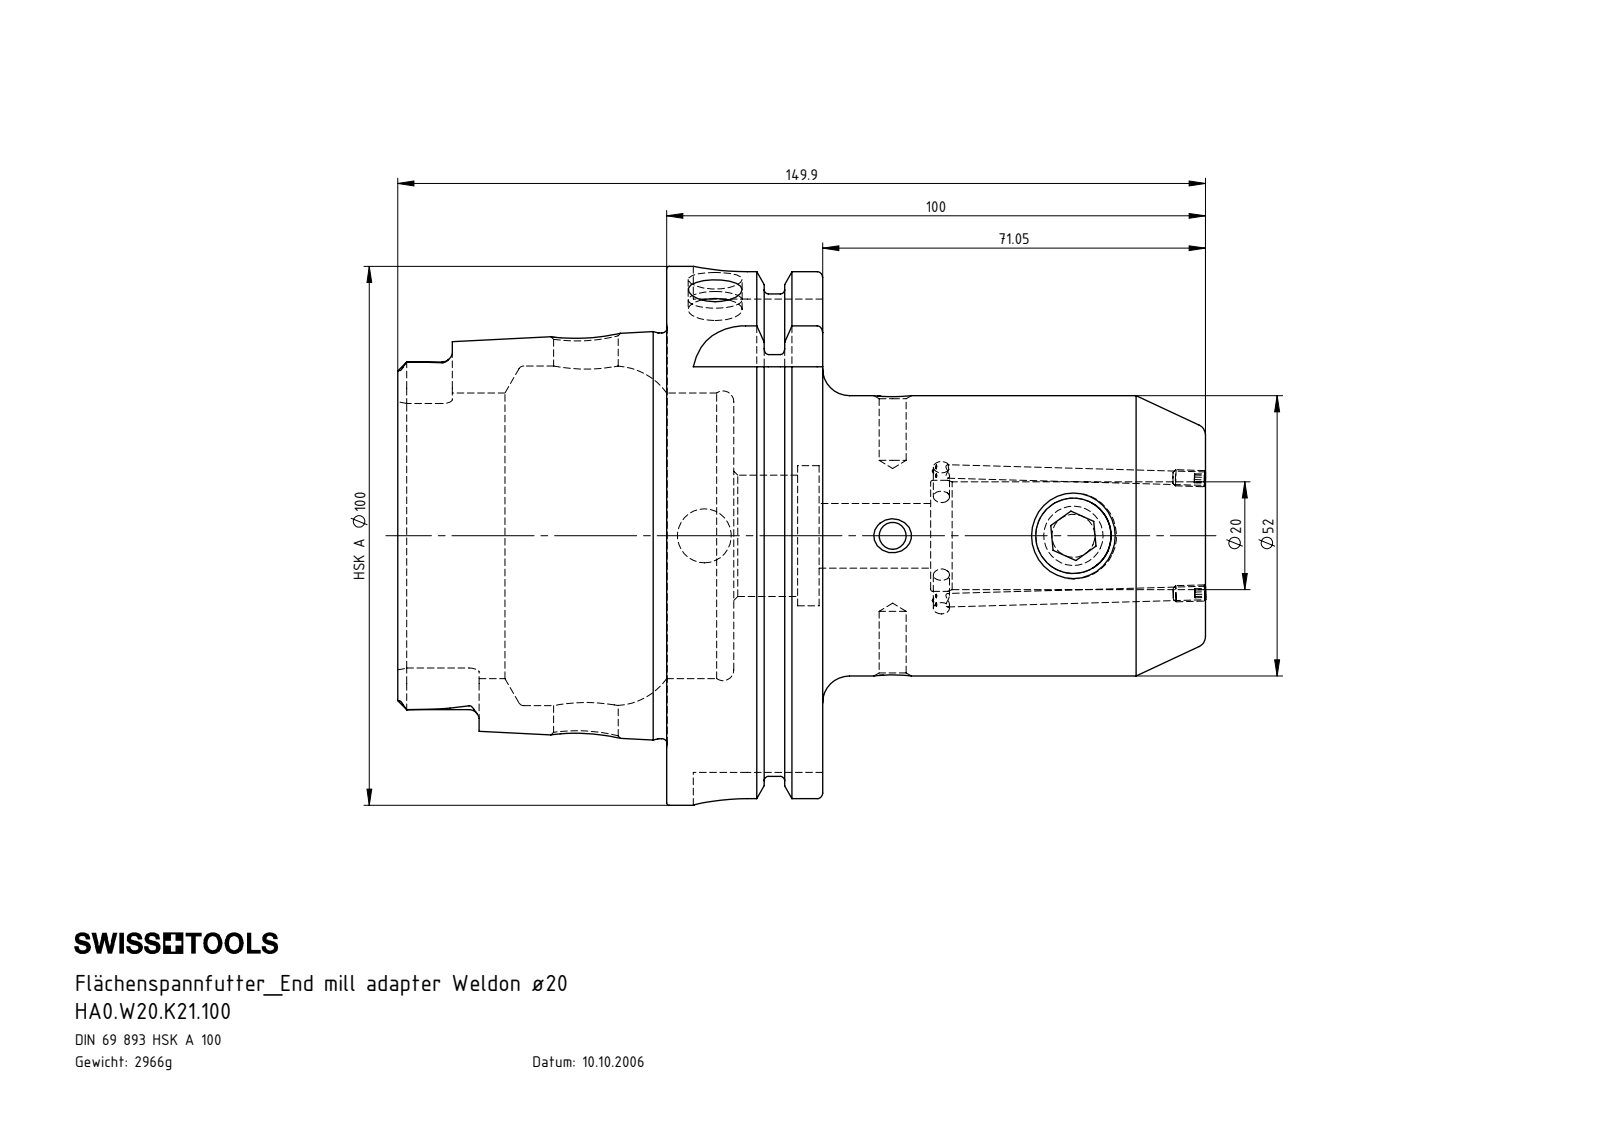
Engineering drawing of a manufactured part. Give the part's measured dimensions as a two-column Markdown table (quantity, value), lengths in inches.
| quantity | value |
| --- | --- |
| part name | HA0.W20.K21.100; ERU-CJ2.001.006; W20-ER1.001.016; HA0-W20.K21.100_D_Fertigbearbeitung |
| STEP written by | SolidWorks 2012 (CONFIG_CONTROL_DESIGN) |
| units | inches |
| bodies | 4 solids, 271 faces (71 planar, 82 cylindrical, 118 other) |
| overall size | 5.905 × 3.937 × 3.937 |
| volume | 23.06 in³ |
| surface area | 105 in² |
| round holes (diameter × count) | 0.394 × 3, 0.098 × 2, 0.197 × 2, 0.472 × 2, 0.118 × 1, 0.551 × 1, 0.787 × 1, 0.811 × 1, 0.886 × 1, 1.024 × 1, 2.087 × 1, 2.48 × 1 |
| round bosses / shafts (diameter × count) | 0.118 × 2, 3.937 × 1, 3.62 × 1, 2.963 × 1, 2.047 × 1, 0.63 × 1 |
| partial cylindrical surfaces (radius × count) | 0.075 × 6, 0.192 × 4, 0.394 × 4 |
| main face-to-face distances | 1.14, 0.65, 0.49, 1.965, 2.455, 3.104, 5.902, 3.937, 3.447, 2.797 |
| hole center spacings | 1.321, 1.376, 2.242, 2.697 |
